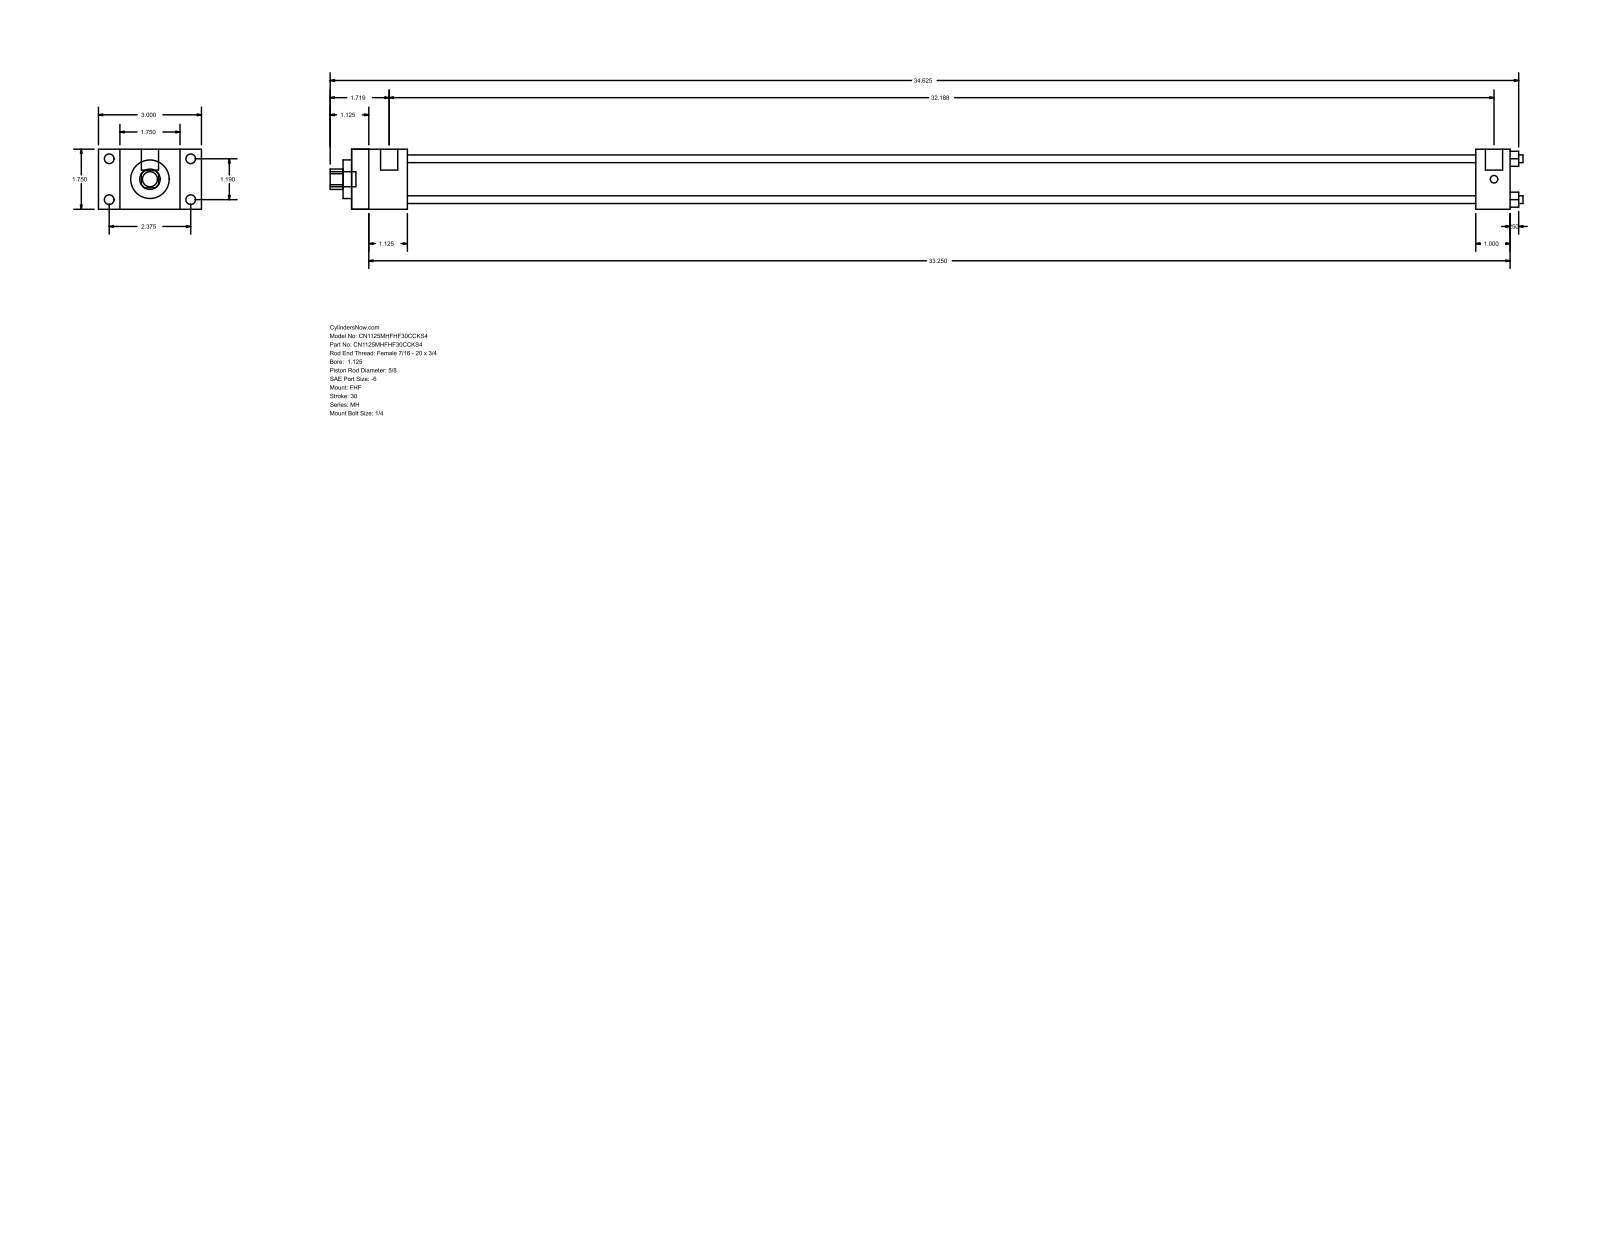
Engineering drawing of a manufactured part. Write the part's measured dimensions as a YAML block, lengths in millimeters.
part_name: "MH_FHF__0112_0.625"
step_written_by: "GSSL Pune (CONFIG_CONTROL_DESIGN)"
units: millimeters
bodies: {solids: 0, faces: 88, planar: 60, cylindrical: 28, other: 0}
overall_size: [882.65, 76.2, 44.45]
round_holes:
  - {diameter: 5.71, count: 4}
  - {diameter: 15.88, count: 1}
  - {diameter: 28.57, count: 1}
  - {diameter: 34.92, count: 1}
round_bosses_or_shafts:
  - {diameter: 7.14, count: 4}
  - {diameter: 5.56, count: 4}
  - {diameter: 12.7, count: 2}
  - {diameter: 11.11, count: 1}
partial_cylinders:
  - {radius: 7.54, count: 1}
face_to_face_distances: [44.46, 15.87, 60.33, 41.27, 76.2, 857.24, 815.97, 831.85, 790.58, 25.39]
hole_center_spacings: [21.37, 30.22, 42.74]
